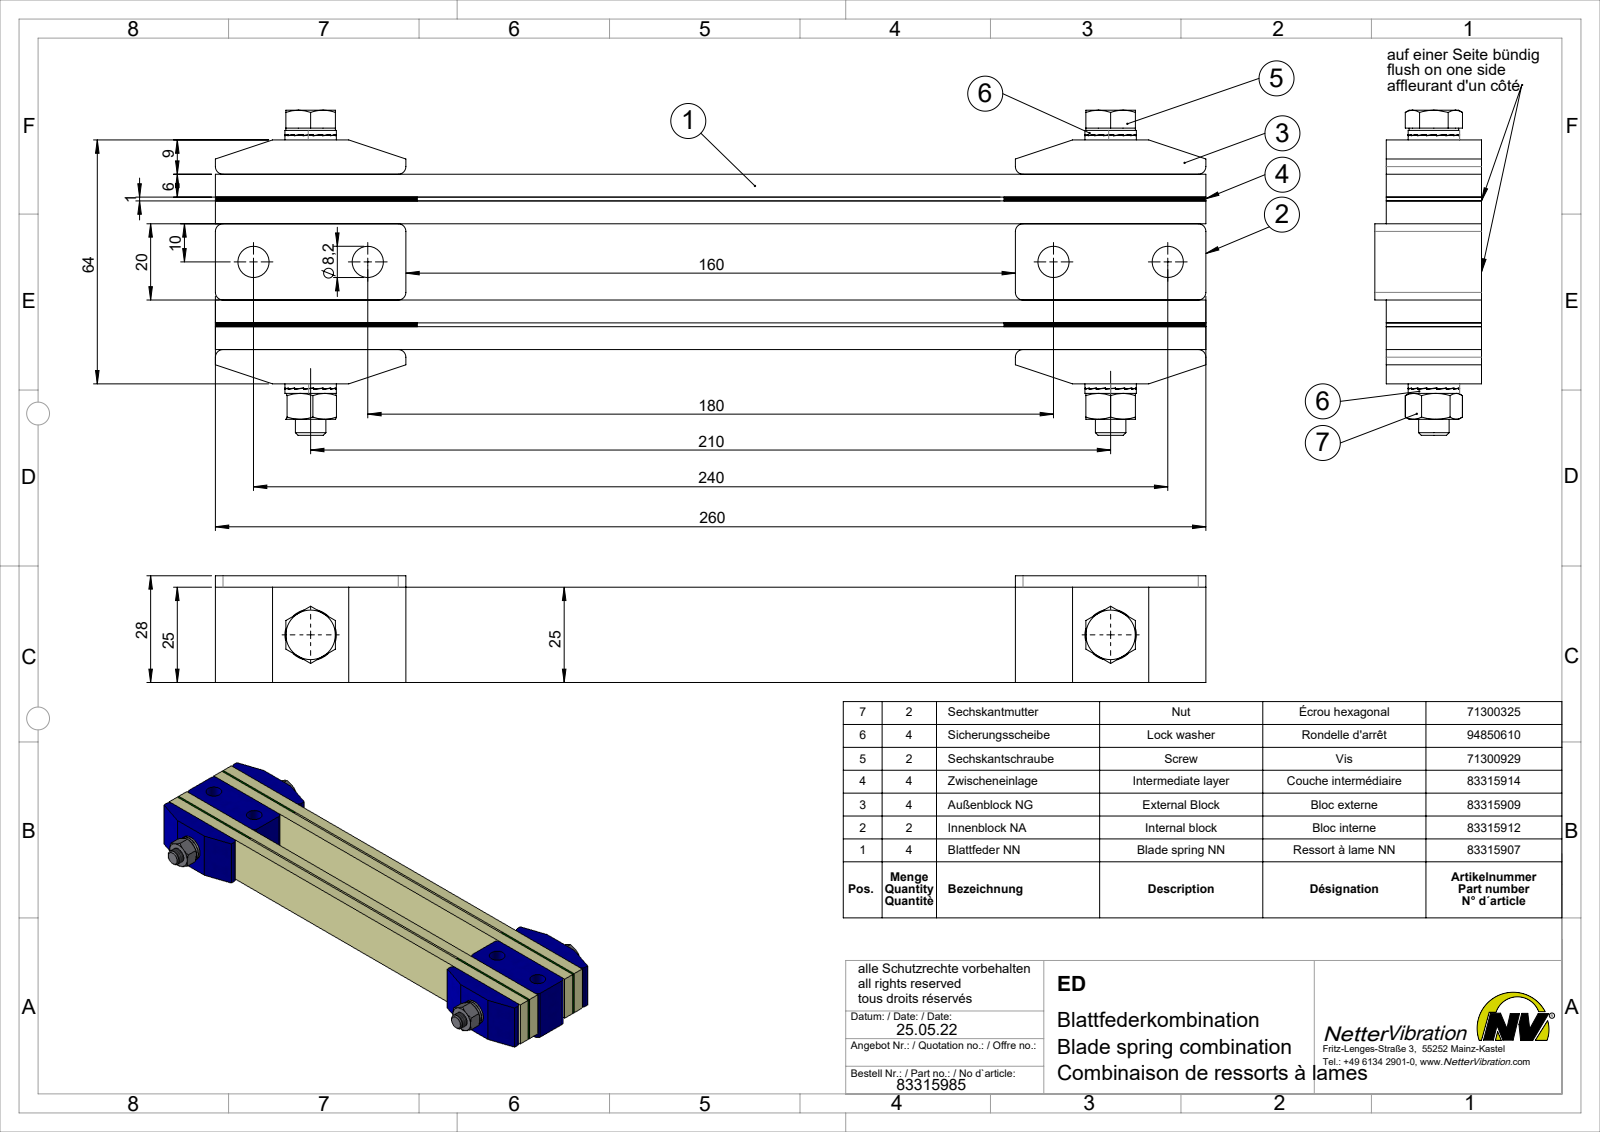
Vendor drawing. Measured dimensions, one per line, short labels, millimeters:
name: Blattfederkombination ED # 83315985
written by: SolidWorks 2015 (AUTOMOTIVE_DESIGN)
unit: mm
bodies: 22 solids, 746 faces (594 planar, 100 cylindrical, 52 other)
size: 260 × 85.3 × 28
volume: 253 442 mm³; area: 114 026 mm²
holes: 6× ⌀8.2, 2× ⌀6.8, 2× ⌀8, 2× ⌀8.5, 2× ⌀8.7
bosses: 2× ⌀13.5, 2× ⌀13
rounds: 16× R2
face distances: 33, 6, 7, 1, 27, 26, 13, 39, 40, 34
hole spacings: 210, 30, 180, 240
